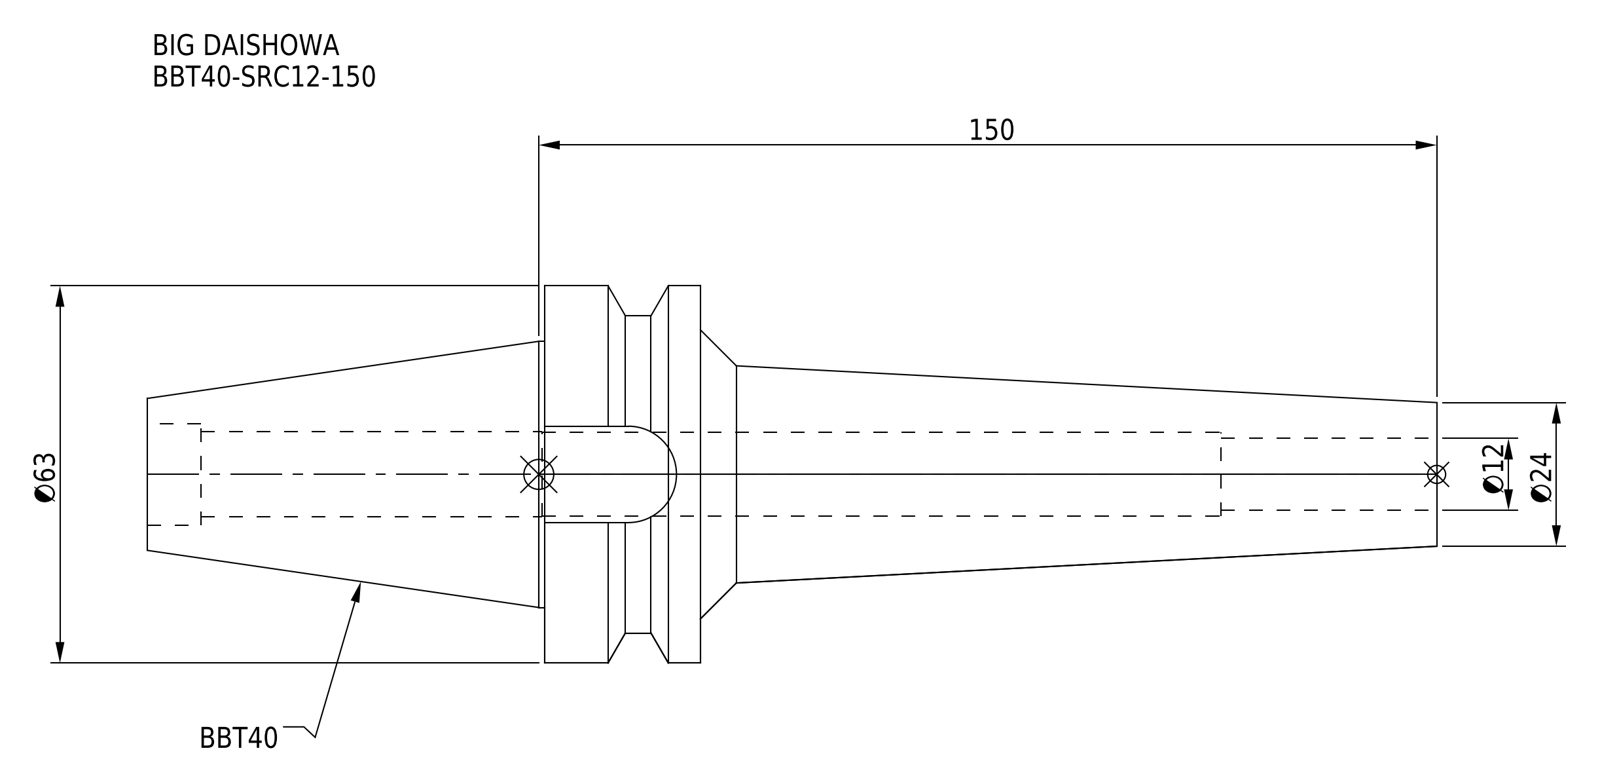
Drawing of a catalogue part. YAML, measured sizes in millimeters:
part_name: "BBT40-SRC12-150"
step_written_by: "CREO PARAMETRIC BY PTC INC, 2016380 (AUTOMOTIVE_DESIGN)"
units: millimeters
bodies: {solids: 1, faces: 43, planar: 13, cylindrical: 20, other: 10}
overall_size: [215.4, 63, 63]
volume: 196038
surface_area: 38794
round_holes:
  - {diameter: 12, count: 1}
  - {diameter: 14, count: 1}
  - {diameter: 14.2, count: 1}
  - {diameter: 17, count: 1}
round_bosses_or_shafts:
  - {diameter: 63, count: 1}
  - {diameter: 53, count: 1}
  - {diameter: 44.45, count: 1}
partial_cylinders:
  - {radius: 8.05, count: 1}
face_to_face_distances: [26, 123, 149, 45, 215.4, 92.4, 66.4, 16.1, 206.4, 83.4]
